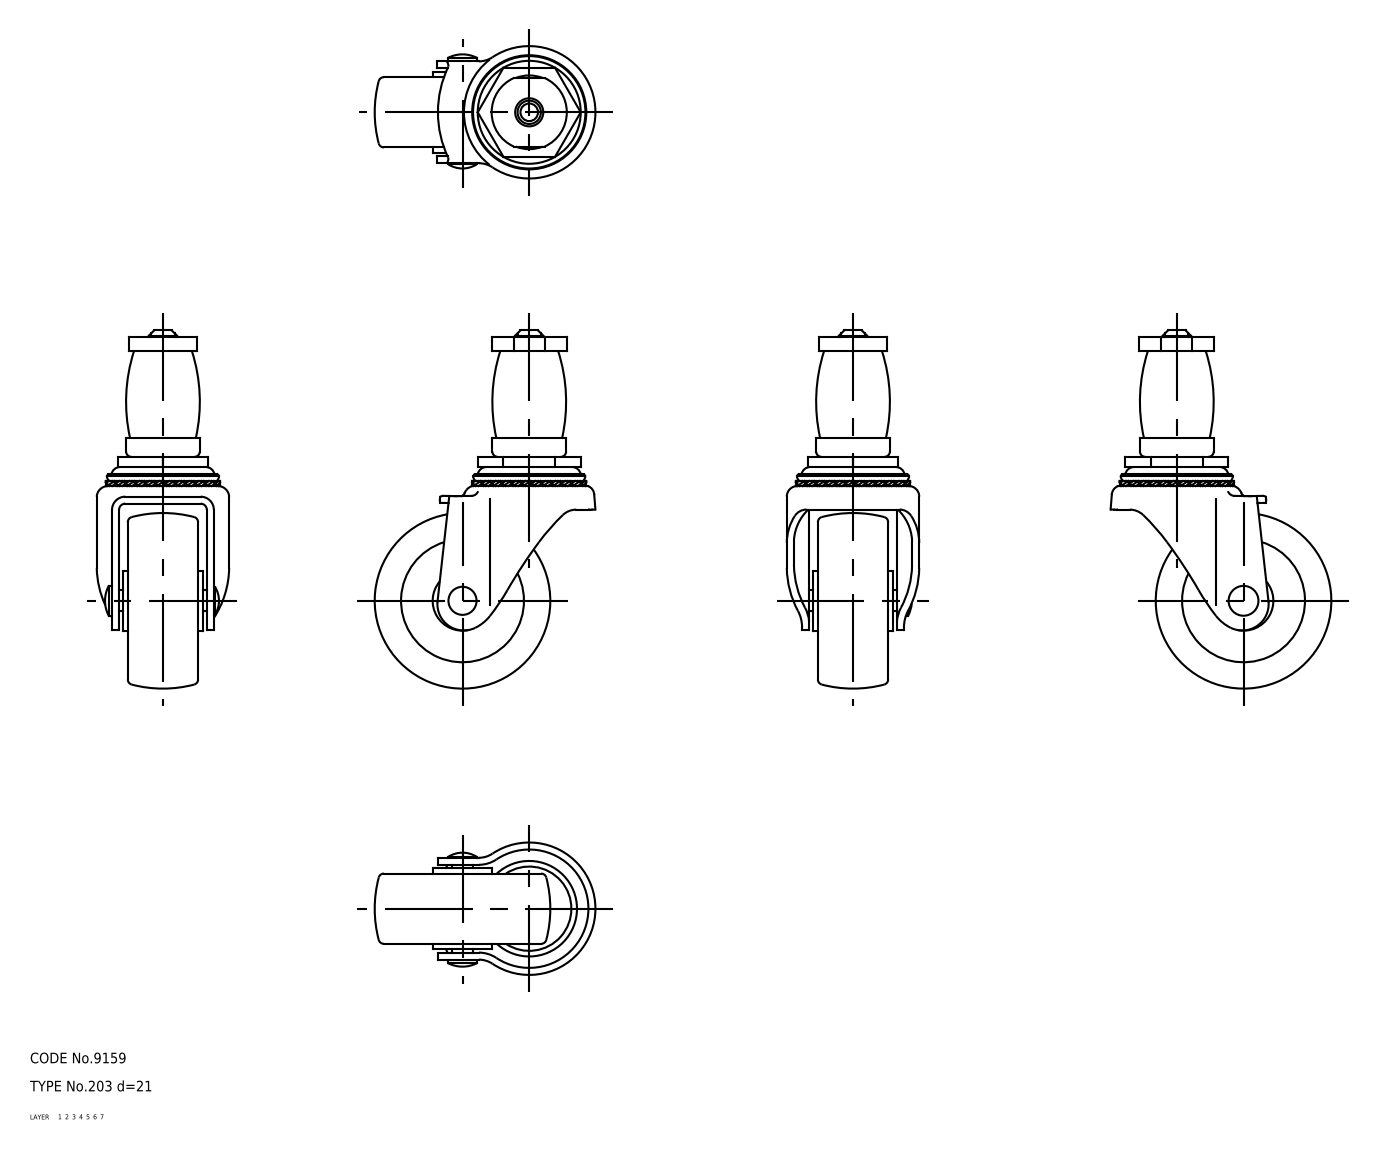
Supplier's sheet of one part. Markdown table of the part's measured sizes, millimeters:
| quantity | value |
| --- | --- |
| part name | wheel; main shaft; axle; No_203_d21_21392_36 |
| STEP written by | CADfix (AUTOMOTIVE_DESIGN) |
| units | millimeters |
| bodies | 4 solids, 185 faces (0 planar, 0 cylindrical, 185 other) |
| overall size | 102 × 62.85 × 37.7 |
| volume | 61 471 mm³ |
| surface area | 20 586 mm² |
